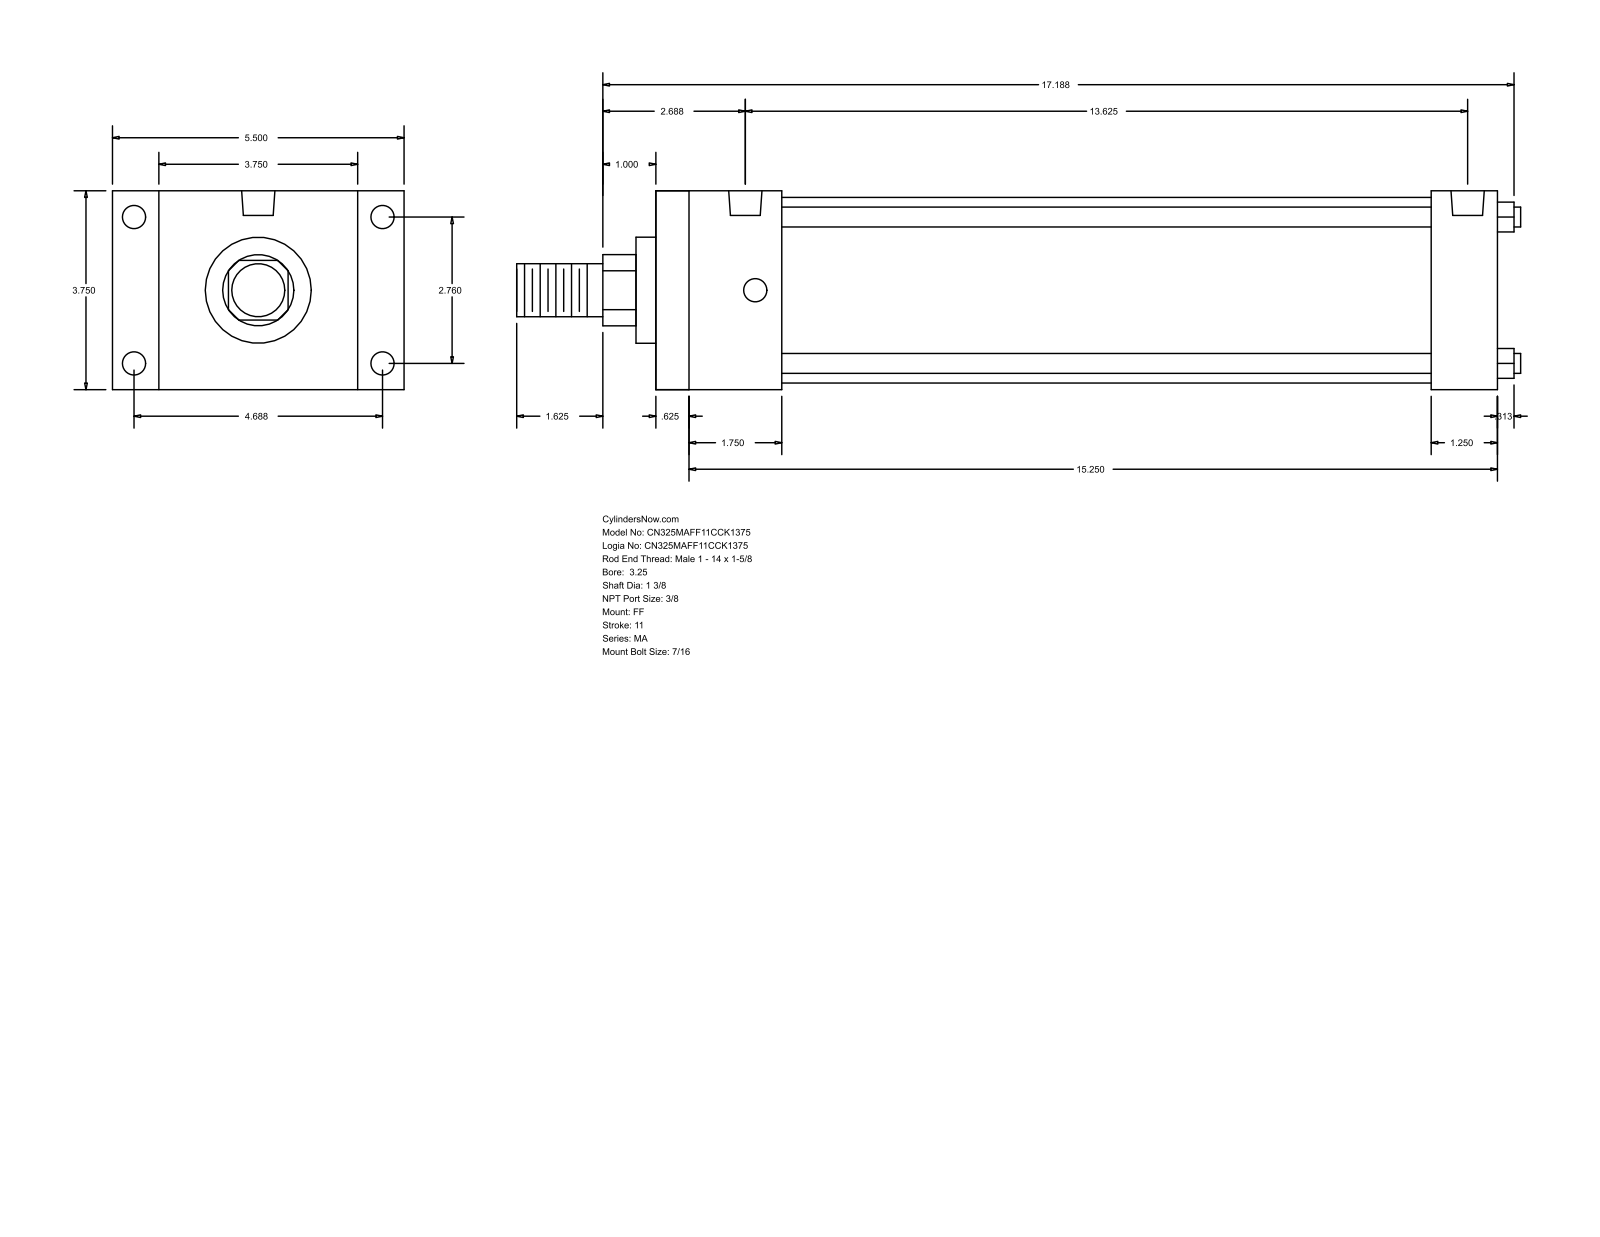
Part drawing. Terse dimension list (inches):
name: MA_FF__0325_1.375
written by: GSSL Pune (CONFIG_CONTROL_DESIGN)
unit: in
bodies: 0 solids, 92 faces (64 planar, 28 cylindrical, 0 other)
size: 18.937 × 5.5 × 3.75
holes: 8× ⌀0.437, 2× ⌀0.627
bosses: 4× ⌀0.375, 1× ⌀3.5, 1× ⌀2, 1× ⌀1.375, 1× ⌀1
rounds: 1× R0.672
face distances: 3.75, 15.875, 0.625, 15.25, 0.875, 4.625, 2.375, 14.625, 1.75, 14
hole spacings: 0.188, 2.76, 4.687, 5.439, 13.25, 13.437, 13.625
